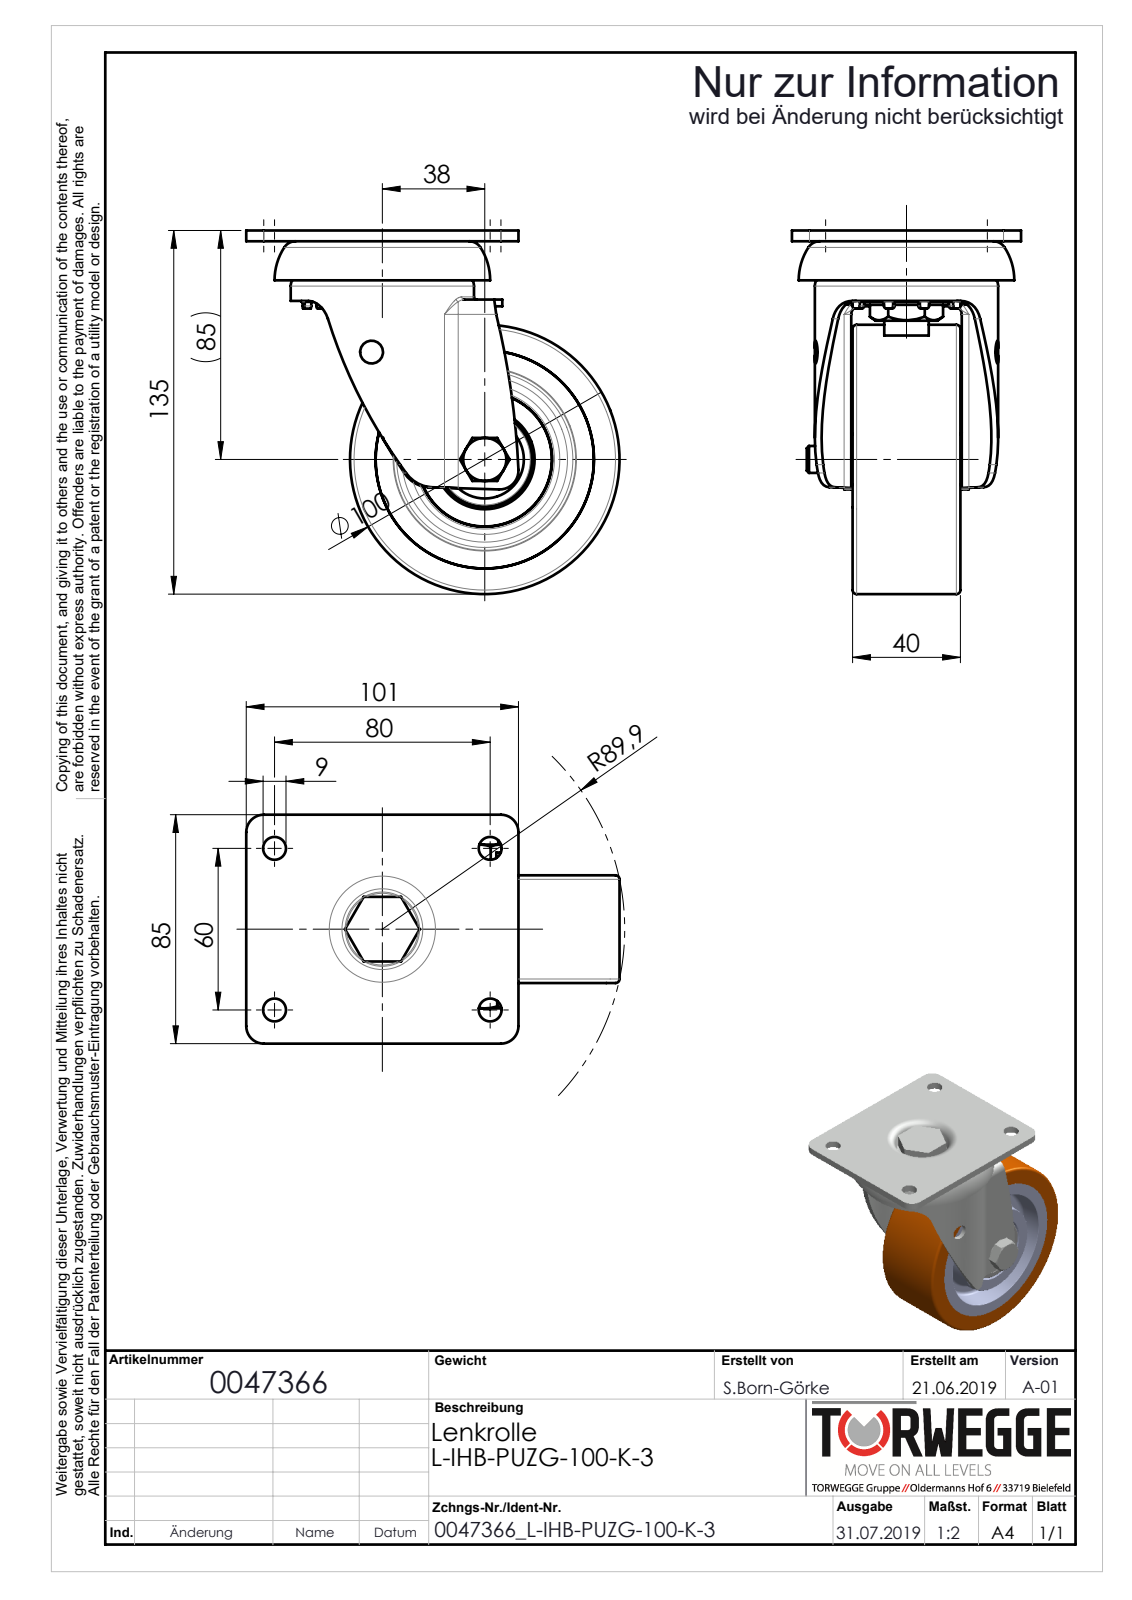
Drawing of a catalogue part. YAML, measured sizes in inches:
part_name: "0047366_L-IHB-PUZG-100-K-3_(A-01)"
step_written_by: "SolidWorks 2018 (AUTOMOTIVE_DESIGN)"
units: inches
bodies: {solids: 0, faces: 523, planar: 167, cylindrical: 171, other: 185}
overall_size: [5.453, 5.315, 3.346]
round_holes:
  - {diameter: 0.335, count: 6}
  - {diameter: 0.394, count: 1}
  - {diameter: 0.407, count: 1}
  - {diameter: 0.413, count: 1}
  - {diameter: 0.591, count: 1}
  - {diameter: 0.63, count: 1}
  - {diameter: 0.827, count: 1}
  - {diameter: 0.984, count: 1}
  - {diameter: 1.142, count: 1}
  - {diameter: 1.378, count: 1}
  - {diameter: 3.189, count: 1}
round_bosses_or_shafts:
  - {diameter: 3.937, count: 1}
  - {diameter: 2.677, count: 1}
  - {diameter: 0.787, count: 1}
  - {diameter: 0.778, count: 1}
  - {diameter: 0.65, count: 1}
  - {diameter: 0.587, count: 1}
partial_cylinders:
  - {radius: 0.039, count: 22}
  - {radius: 0.256, count: 4}
  - {radius: 0.118, count: 2}
  - {radius: 0.217, count: 2}
  - {radius: 0.295, count: 2}
  - {radius: 0.394, count: 2}
  - {radius: 0.276, count: 1}
  - {radius: 1.083, count: 1}
face_to_face_distances: [1.575, 0.157, 0.02, 1.142, 0.098, 1.161, 0.118, 1.693, 1.713, 1.594]
hole_center_spacings: [2.28, 2.362, 3.15, 3.937]
